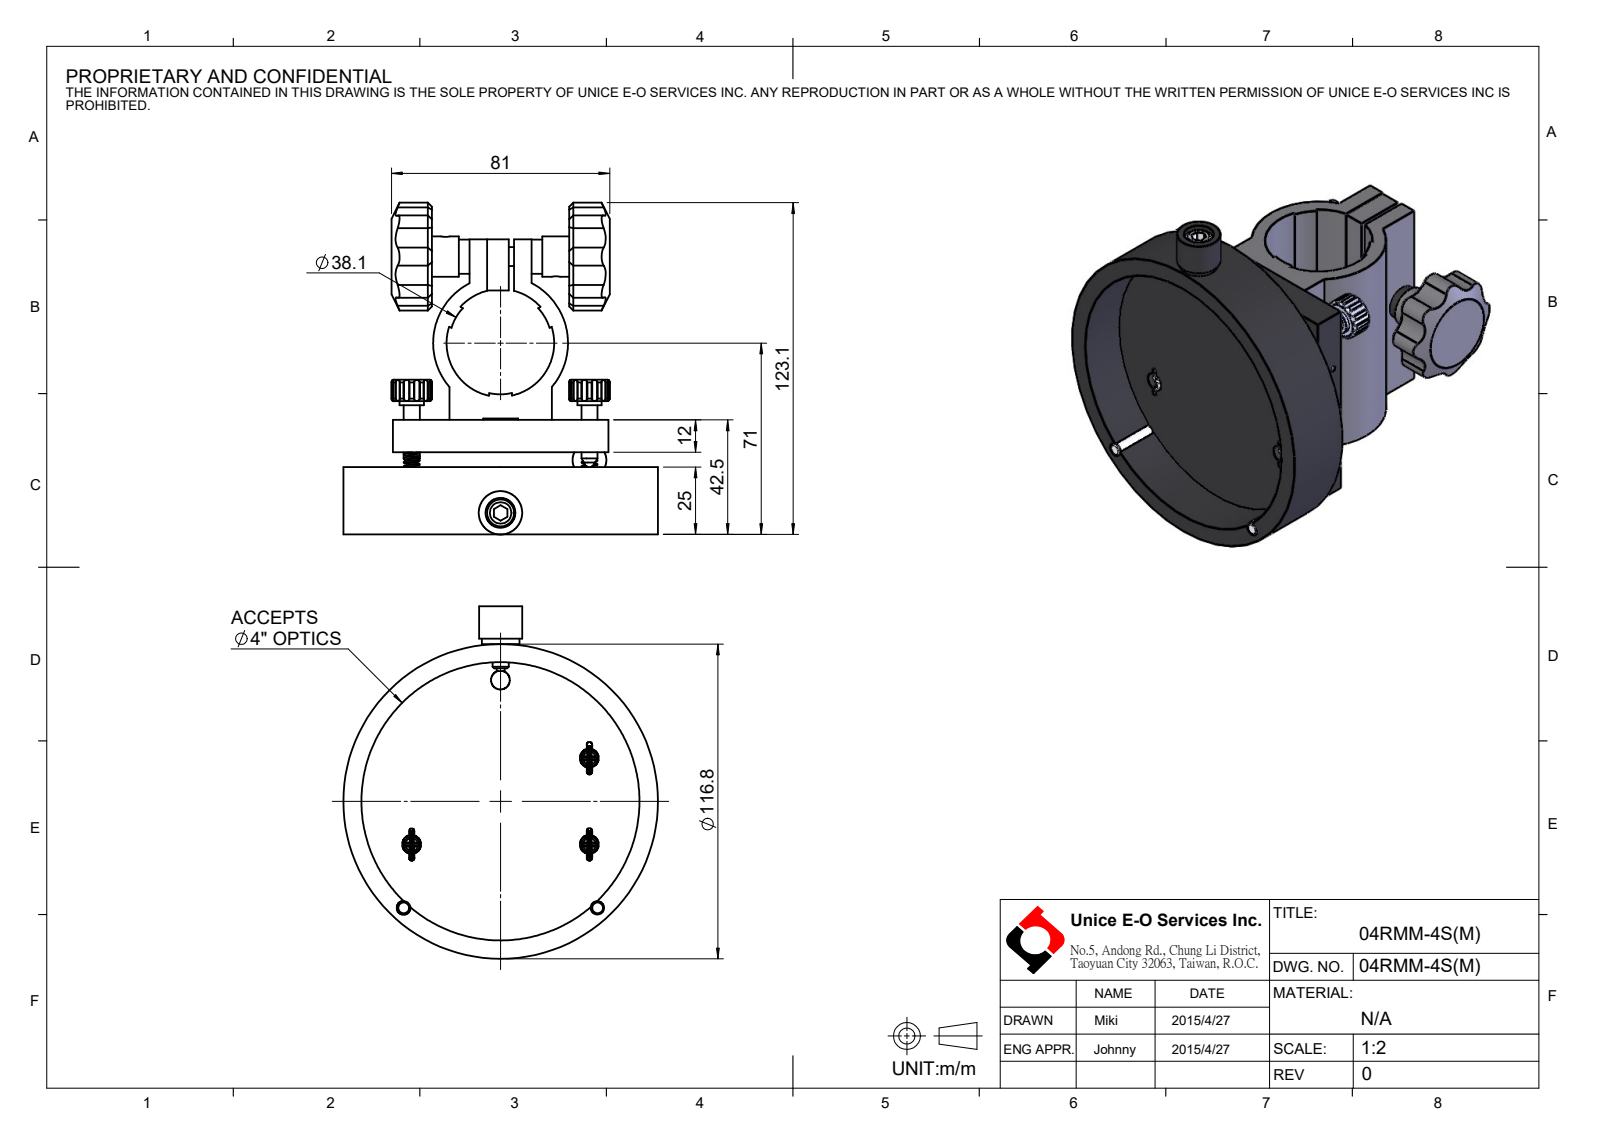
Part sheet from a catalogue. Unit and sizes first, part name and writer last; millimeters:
Units: millimetres
Overall size (bounding box): 130.8 × 123.1 × 116.8
Round holes (diameter × count): ⌀5 ×12, ⌀3.3 ×6, ⌀7 ×5, ⌀1.2 ×4, ⌀4.5 ×4, ⌀8 ×4, ⌀11 ×4, ⌀6.6 ×3, ⌀2 ×2, ⌀4 ×2, ⌀4.7 ×2, ⌀5.9 ×2
Round bosses / shafts (diameter × count): ⌀0.6 ×6, ⌀7 ×4, ⌀4 ×4, ⌀1.6 ×4, ⌀9 ×2, ⌀6 ×2, ⌀116.8 ×1, ⌀16 ×1
Partial cylindrical surfaces — rounded edges, fillets, slot ends (radius × count): R0.3 ×48, R1.5 ×24, R4 ×8, R7 ×8, R1 ×6, R7.5 ×2, R19.05 ×1, R20 ×1
Main face-to-face distances: 7.2, 17.5, 24.7, 5.5, 12, 12.7, 30.5, 6.5, 14, 25
Hole centre spacings: 12.5, 27.95, 25, 50, 17.68, 26.25, 32.33, 36.67
Volume: 322 511 mm³ · Surface area: 111 718 mm²
Bodies: 37 solids, 596 faces (229 planar, 258 cylindrical, 109 other)
Part name (STEP PRODUCT): 04RMM-4S(M)
STEP written by: SolidWorks 2022 (CONFIG_CONTROL_DESIGN)
